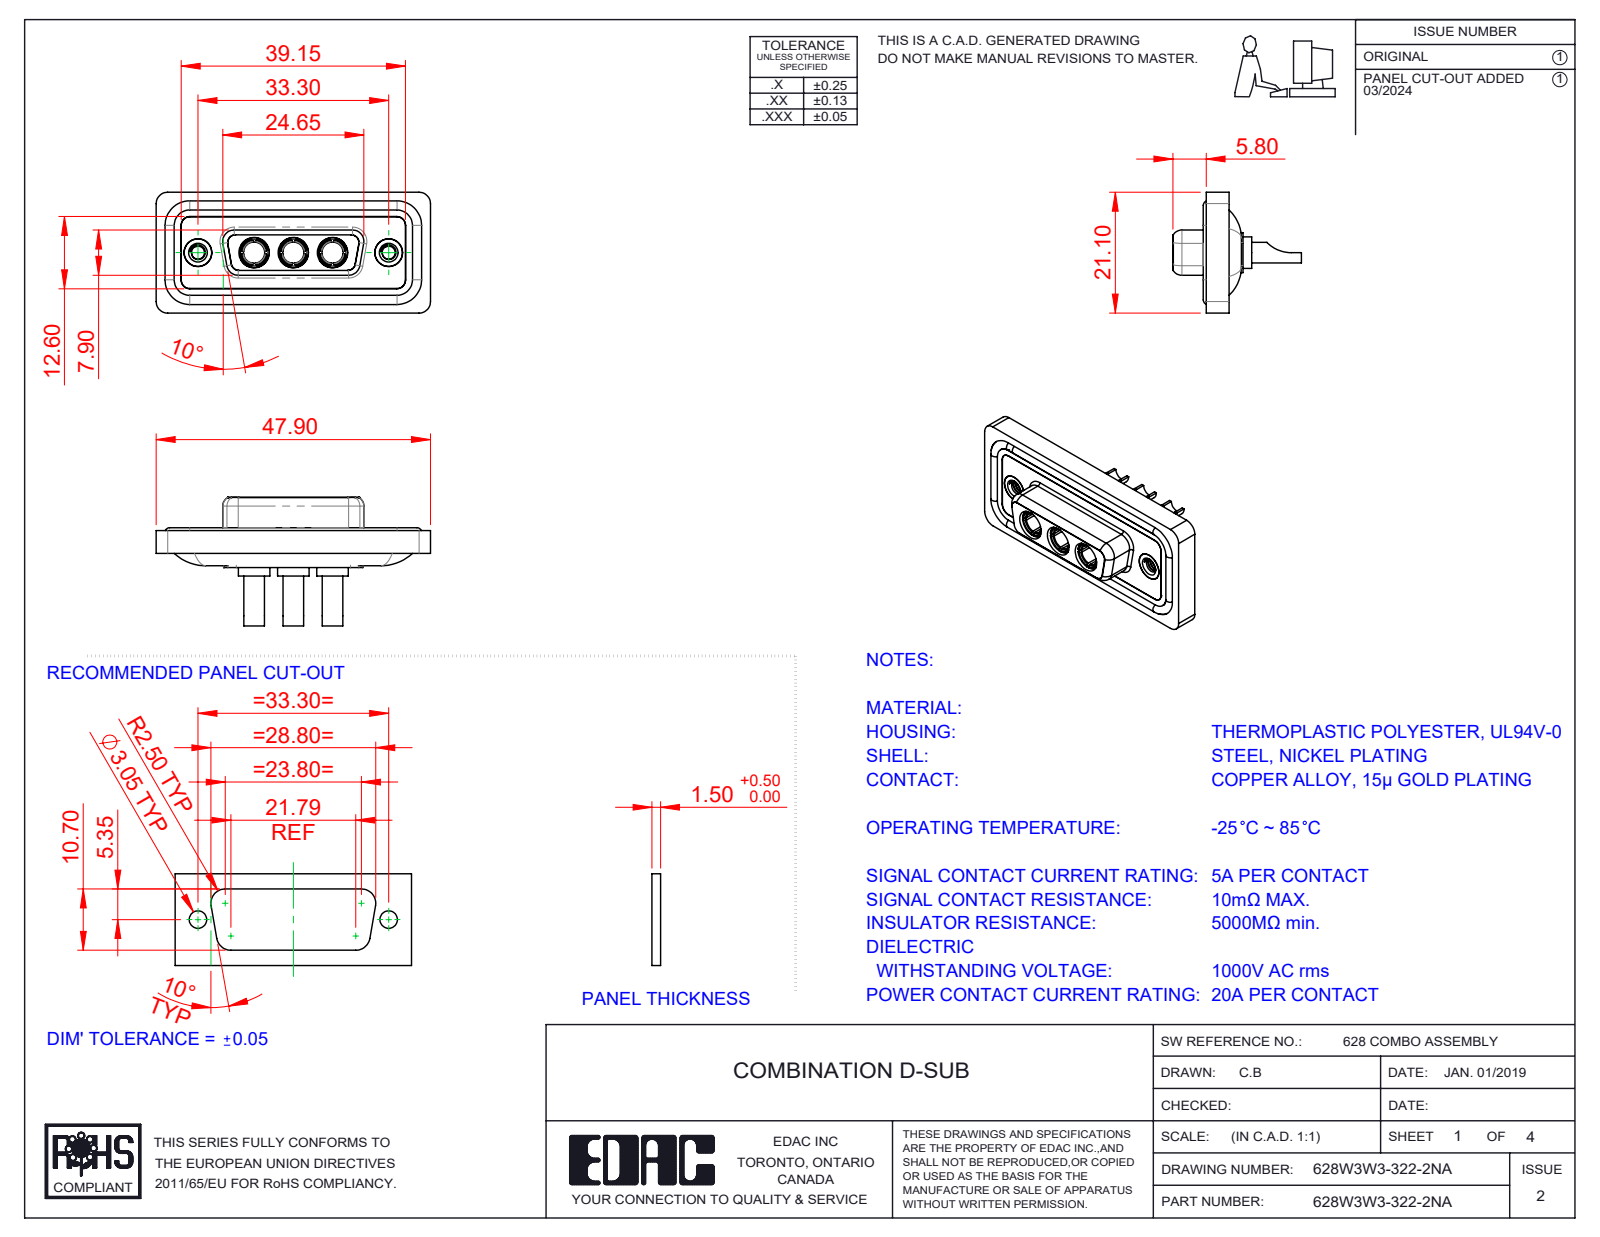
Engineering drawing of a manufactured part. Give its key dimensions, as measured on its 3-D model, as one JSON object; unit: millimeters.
{"part_name": "628Combo Waterproof Housing_15 Contacts; 628W3W3-322-2NA; 628Combo Housing_3W3; Power Socket_20A SC (+3 more)", "step_written_by": "SolidWorks 2023 (CONFIG_CONTROL_DESIGN)", "units": "millimeters", "bodies": {"solids": 13, "faces": 624, "planar": 201, "cylindrical": 268, "other": 155}, "overall_size": [47.9, 22.45, 21.1], "volume_mm3": 6066, "surface_area_mm2": 9984, "round_holes": [[4.85, 5], [2.7, 3], [3.7, 3], [5.3, 3], [2.26, 2], [4, 2], [4.05, 2], [5, 2]], "round_bosses_or_shafts": [[1.6, 4], [5.5, 3], [5.2, 3], [4.96, 3], [4.75, 3], [3.75, 3], [3.6, 3], [4.95, 2]], "partial_cylinders_radius": [[1.5, 22], [2, 20], [1.35, 12], [1.6, 8], [0.25, 4], [0.5, 4], [0.6, 4], [0.65, 4]], "face_to_face_distances": [0.4, 1.8, 1.6, 0.5, 7.45, 1.1, 2.9, 5.65, 7.05, 6.6], "hole_center_spacings": [6.85, 9.8, 16.65, 23.5, 13.7, 33.3]}
